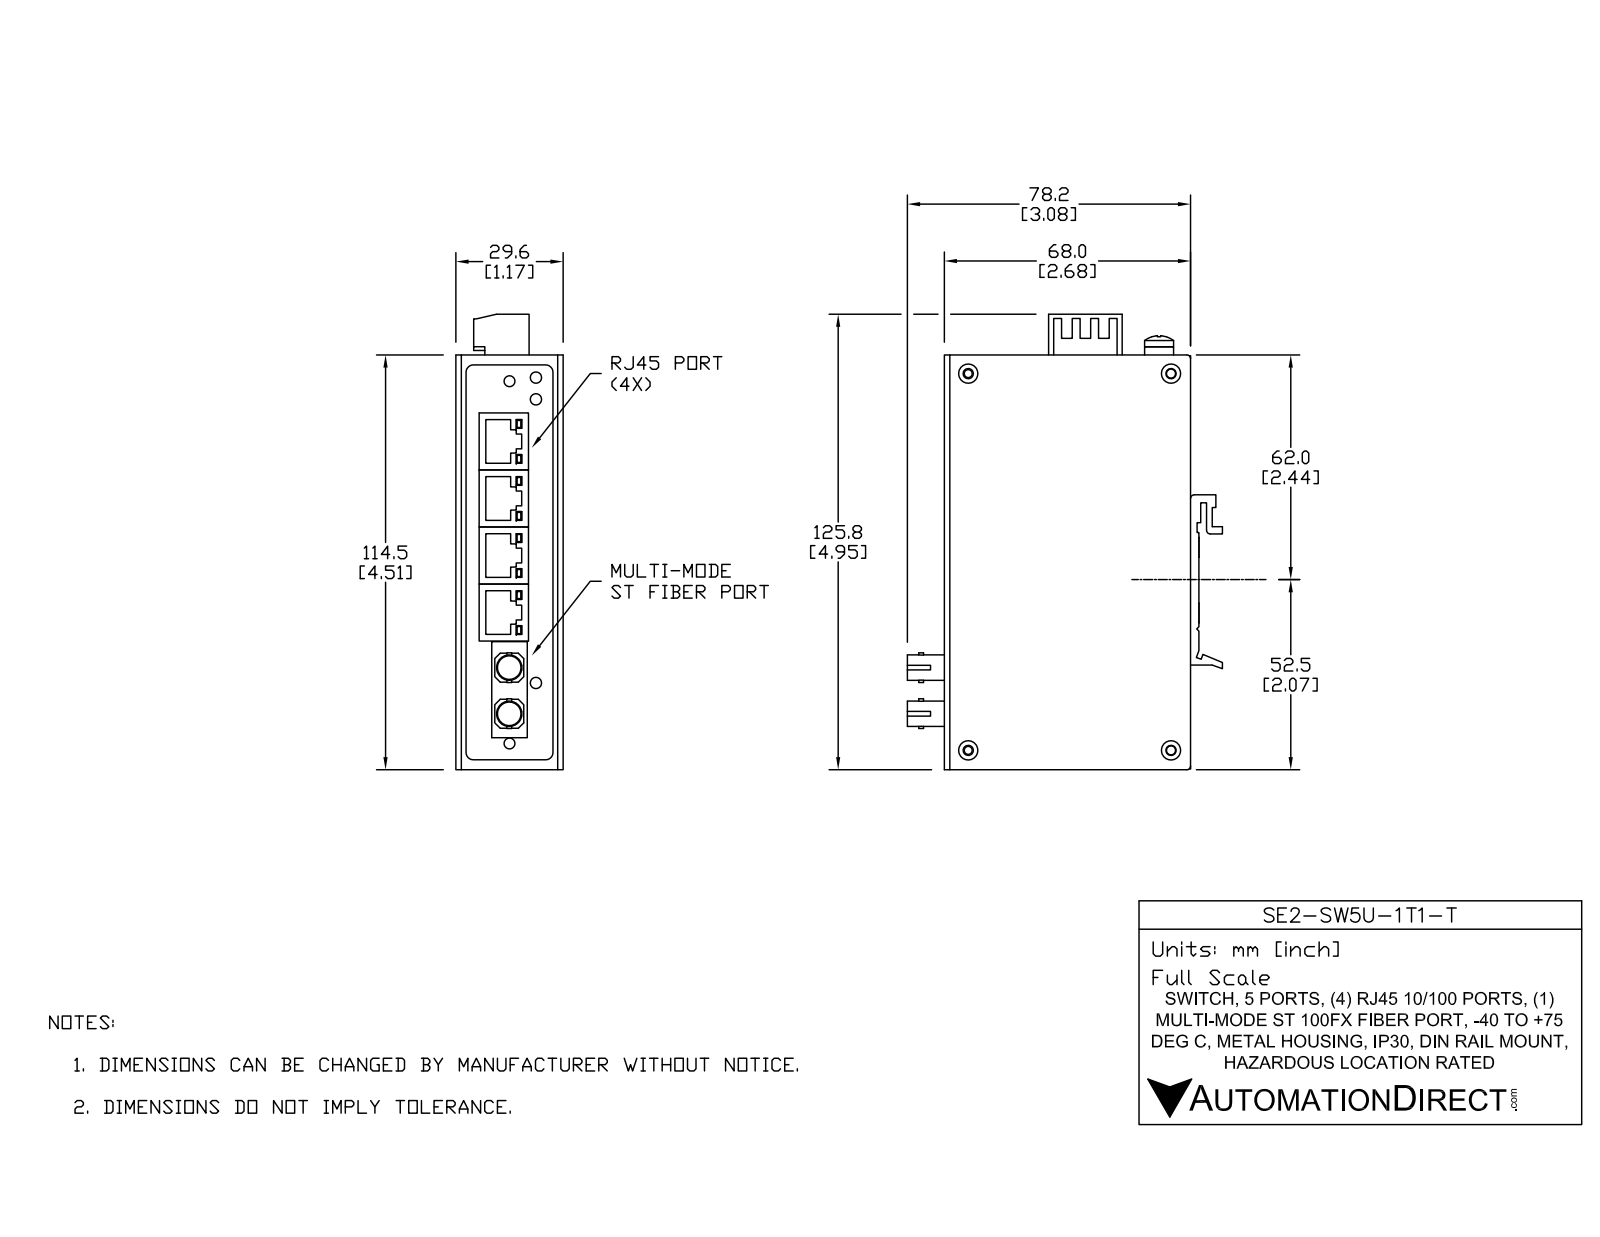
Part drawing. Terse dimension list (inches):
name: SE2-SW5U-1T1-T
written by: SolidWorks 2017 (AUTOMOTIVE_DESIGN)
unit: in
bodies: 13 solids, 939 faces (638 planar, 254 cylindrical, 47 other)
size: 4.951 × 3.425 × 1.165
volume: 2.955 in³; area: 132.6 in²
holes: 4× ⌀0.11, 4× ⌀0.15, 3× ⌀0.122, 2× ⌀0.118, 2× ⌀0.134, 2× ⌀0.256, 1× ⌀0.155
bosses: 4× ⌀0.142, 2× ⌀0.276, 2× ⌀0.217, 2× ⌀0.197, 2× ⌀0.118, 1× ⌀0.315, 1× ⌀0.157, 1× ⌀0.051
rounds: 96× R0.024, 18× R0.008, 16× R0.026, 8× R0.079, 8× R0.118, 6× R0.041, 5× R0.039, 4× R0.012
face distances: 0.039, 0.02, 1.087, 1.126, 0.079, 1.106, 1.067, 0.059, 1.047, 1.165
hole spacings: 0.203, 0.4, 2.205, 4.094, 4.65, 0.197, 0.236, 0.29
